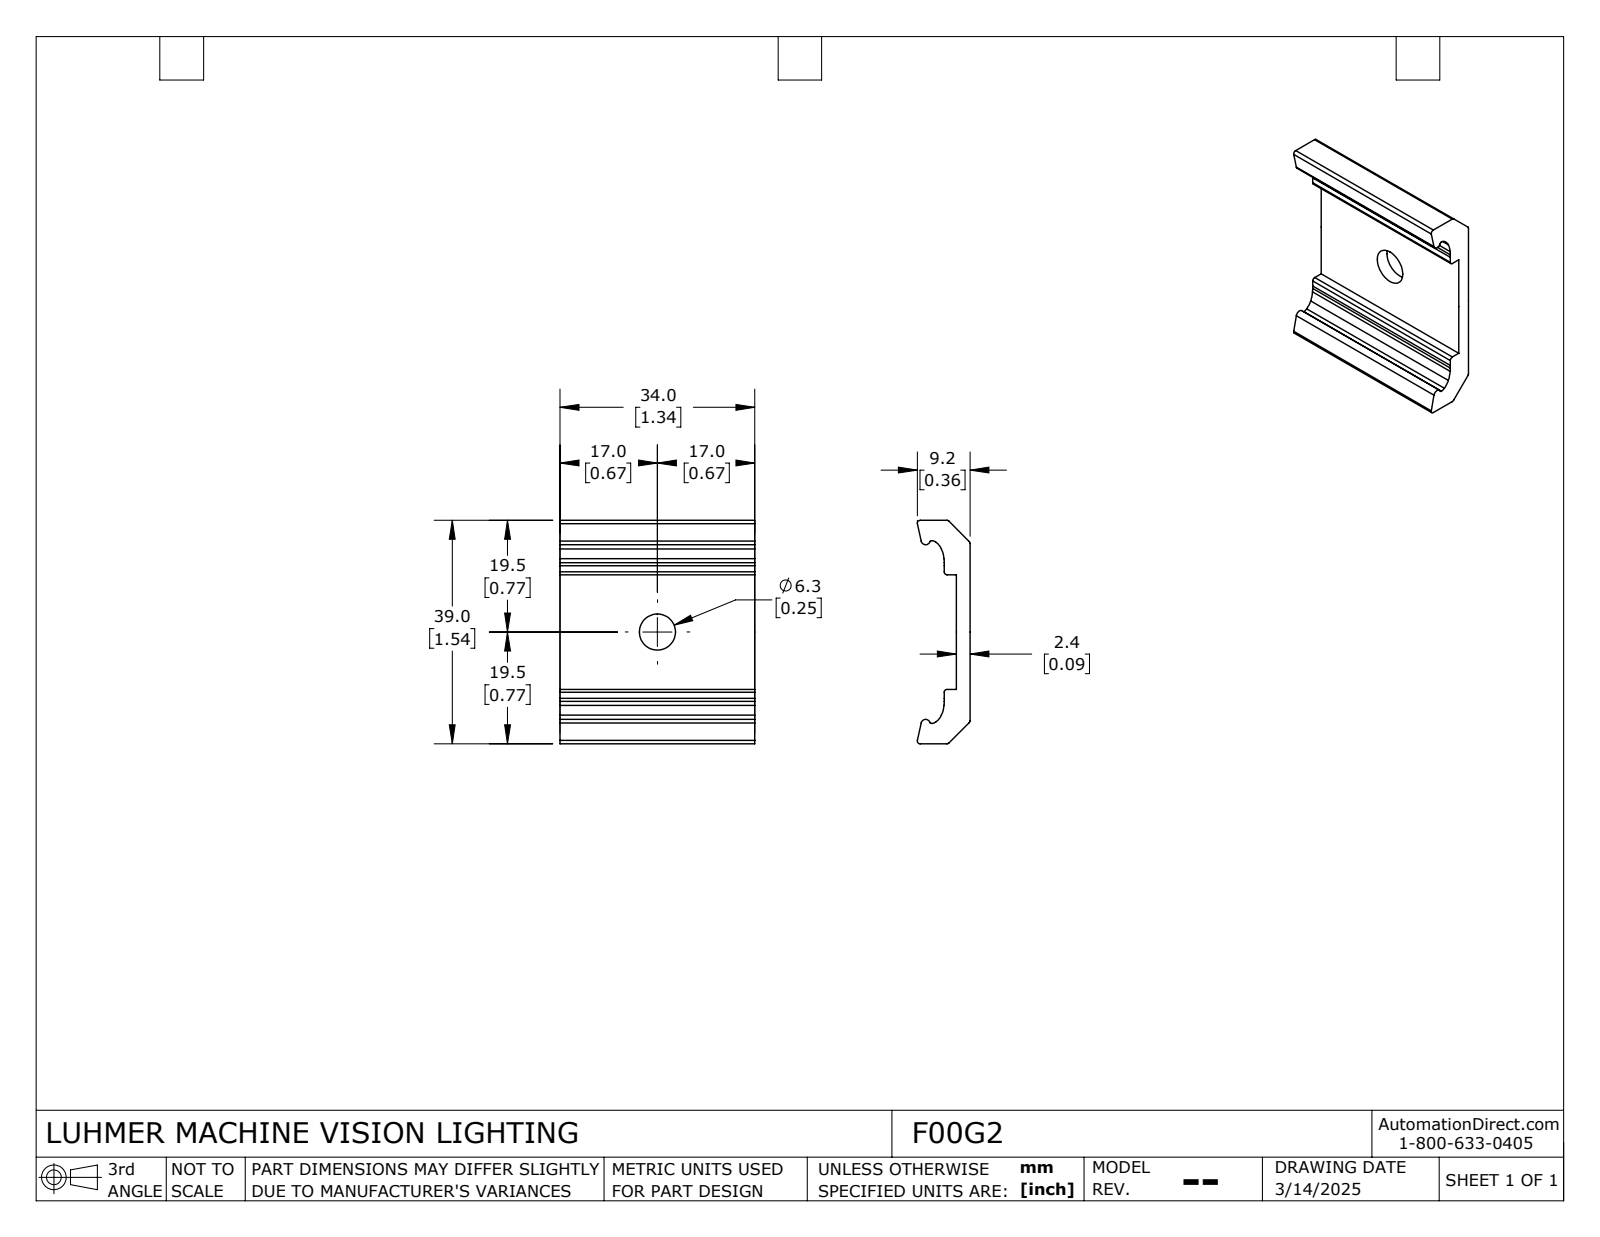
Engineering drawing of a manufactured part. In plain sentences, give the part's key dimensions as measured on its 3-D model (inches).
The part is named "F00G2". Its 3-D file was written by "SolidWorks 2024 (AUTOMOTIVE_DESIGN)". It is 1 solid with 41 faces: 18 planar, 23 cylindrical and 0 other. Overall it measures 1.536 by 1.339 by 0.362 inches. Its volume is 0.318 cubic inches and its surface area 5.851 square inches. Round holes: 1 of diameter 0.248. Partial cylindrical surfaces (rounded edges, fillets, slot ends): 8 of radius 0.02, 2 of radius 0.012, 2 of radius 0.031, 2 of radius 0.055, 2 of radius 0.122, 2 of radius 0.201, 2 of radius 0.398, 2 of radius 1.185. The main face-to-face distances are 0.094, 1.535, 1.339, 0.374, 1.161, 0.177, 0.083, 0.787.
